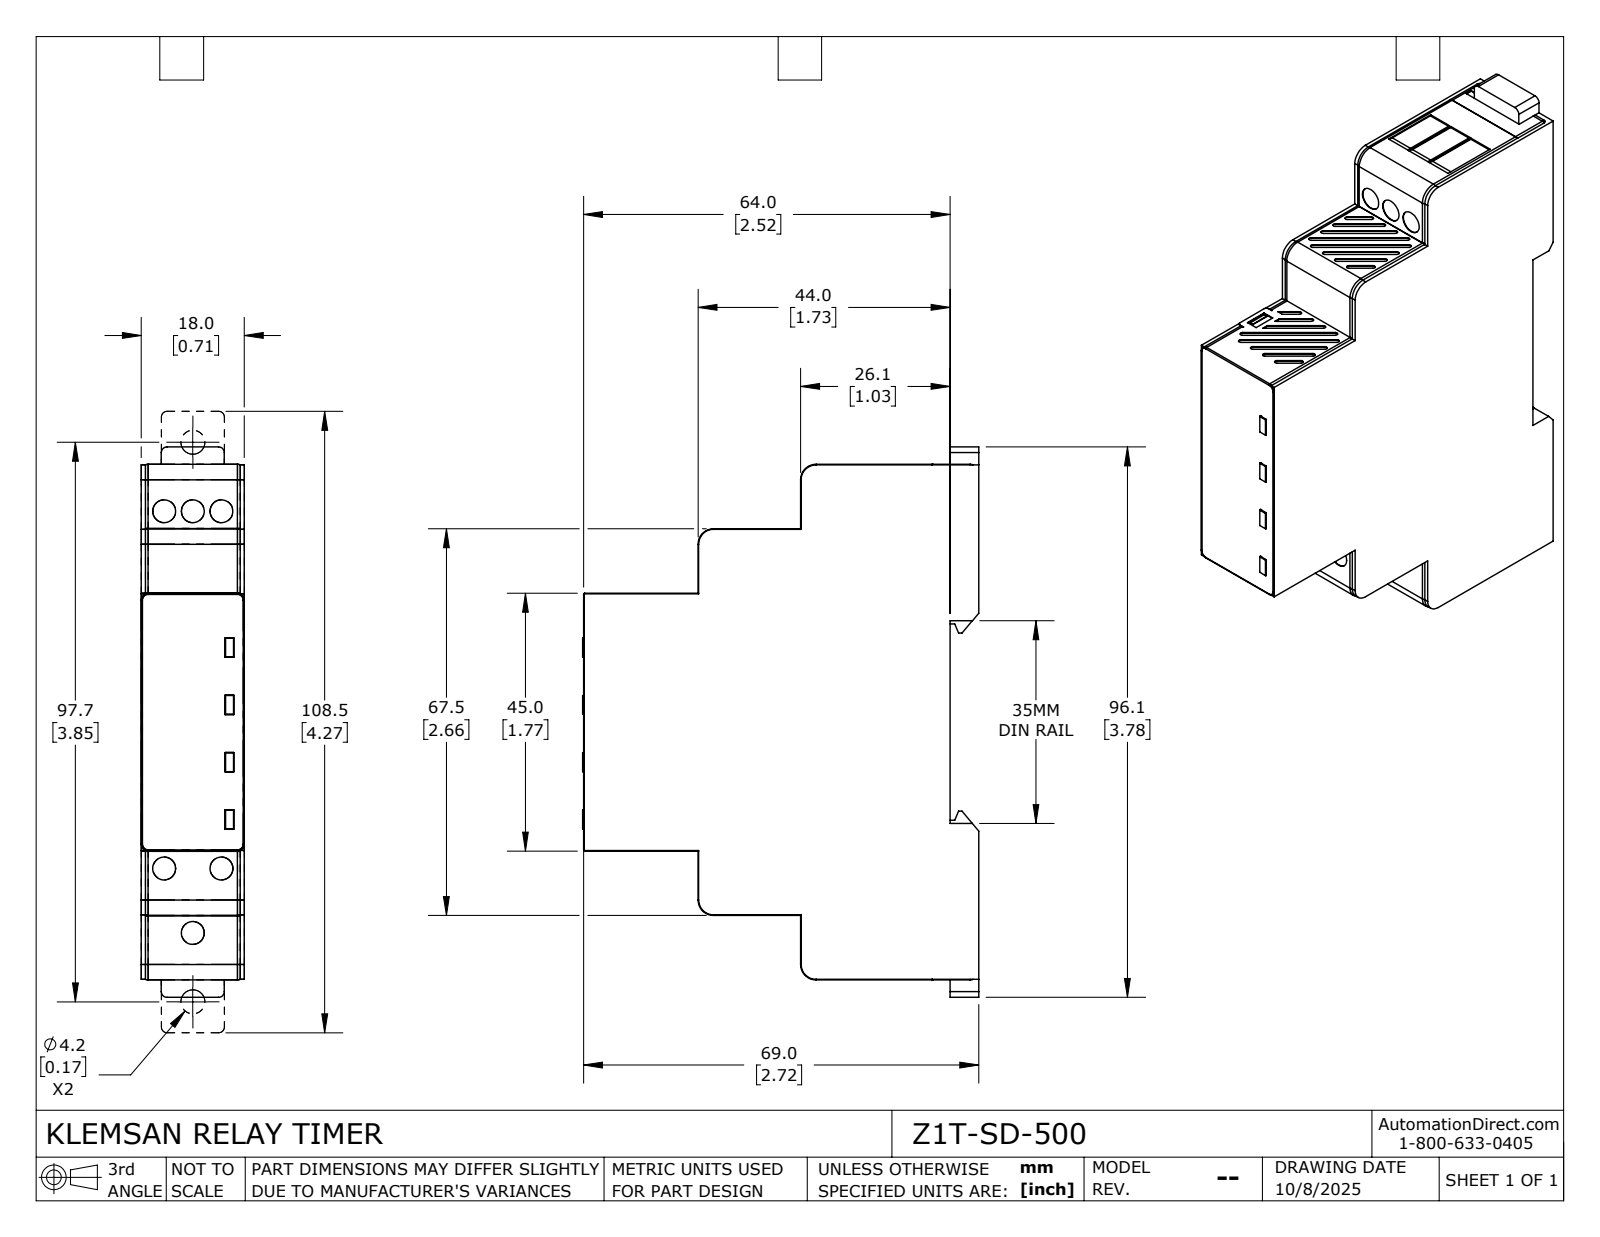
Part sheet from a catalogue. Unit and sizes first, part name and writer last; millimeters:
Units: millimetres
Overall size (bounding box): 96.07 × 69.15 × 18
Round holes (diameter × count): ⌀4.2 ×2, ⌀4 ×1
Partial cylindrical surfaces — rounded edges, fillets, slot ends (radius × count): R1.2 ×16, R0.2 ×4, R1 ×4, R2.6 ×4, R2.7 ×4, R0.5 ×2, R1.5 ×2
Main face-to-face distances: 18, 3.5, 14.5, 11.25, 64, 5, 69, 22.5, 67.4, 67.5
Hole centre spacings: 5.83, 79.43, 85.26
Volume: 83 847 mm³ · Surface area: 17 884 mm²
Bodies: 3 solids, 440 faces (280 planar, 60 cylindrical, 100 other)
Part name (STEP PRODUCT): Z1T-SD-500
STEP written by: SolidWorks 2024 (CONFIG_CONTROL_DESIGN)
